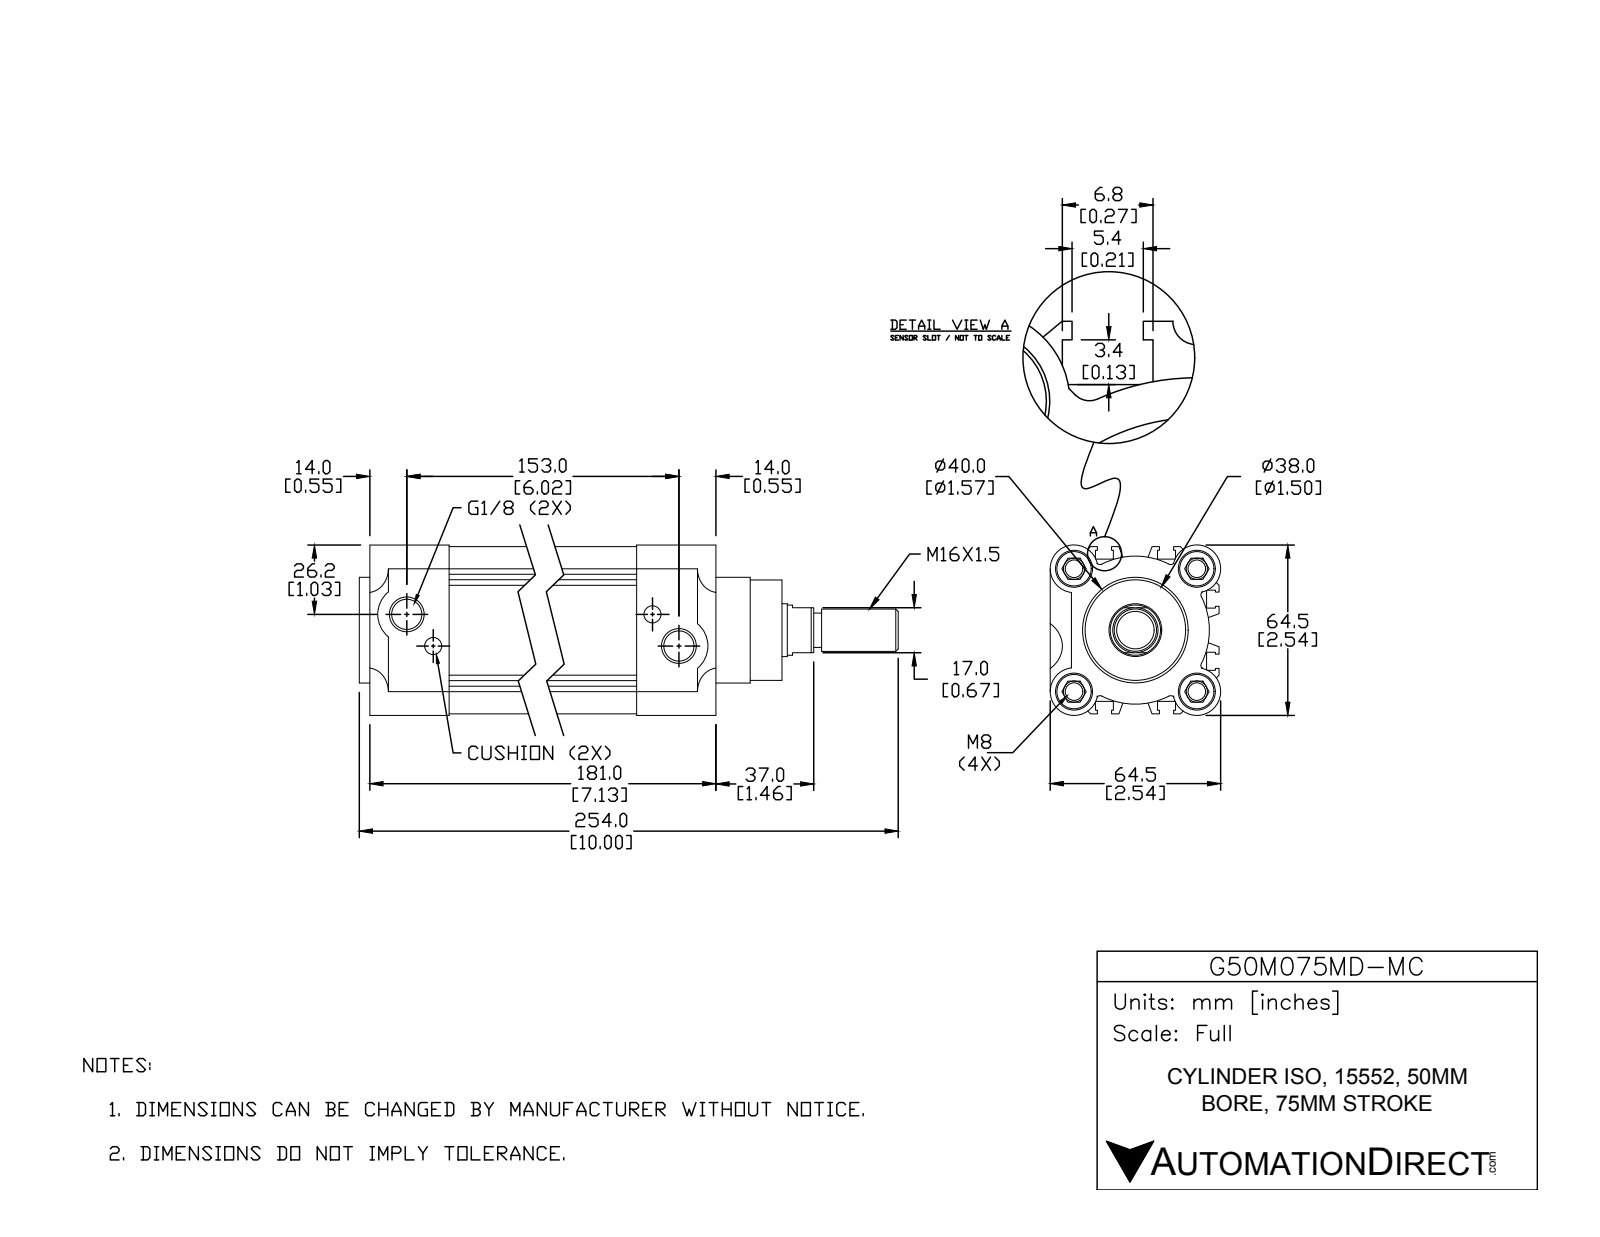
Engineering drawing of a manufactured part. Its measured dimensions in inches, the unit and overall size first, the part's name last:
Units: inches
Overall size (bounding box): 10 × 2.539 × 2.539
Round holes (diameter × count): ⌀0.262 ×4, ⌀0.551 ×4, ⌀0.256 ×2, ⌀0.262 ×2, ⌀0.451 ×2, ⌀0.787 ×1
Round bosses / shafts (diameter × count): ⌀0.512 ×5, ⌀1.969 ×1, ⌀1.575 ×1, ⌀1.496 ×1, ⌀0.748 ×1, ⌀0.63 ×1
Partial cylindrical surfaces — rounded edges, fillets, slot ends (radius × count): R0.059 ×12, R0.004 ×6, R0.331 ×4, R0.354 ×4, R0.433 ×2, R1.083 ×1, R1.102 ×1
Main face-to-face distances: 0.187, 2.305, 0.276, 4.488, 2.492, 4.764, 0.925, 1.062, 1.645, 1.457
Hole centre spacings: 1.294, 1.831, 0.615, 2.589, 5.63, 5.257, 6.042
Volume: 33.65 in³ · Surface area: 221.4 in²
Bodies: 4 solids, 418 faces (236 planar, 138 cylindrical, 44 other)
Part name (STEP PRODUCT): 50-75-90.5-B; 50121-HR; G50M075MD-MC; 5012175-R (+1 more)
STEP written by: SolidWorks 2015 (CONFIG_CONTROL_DESIGN)
